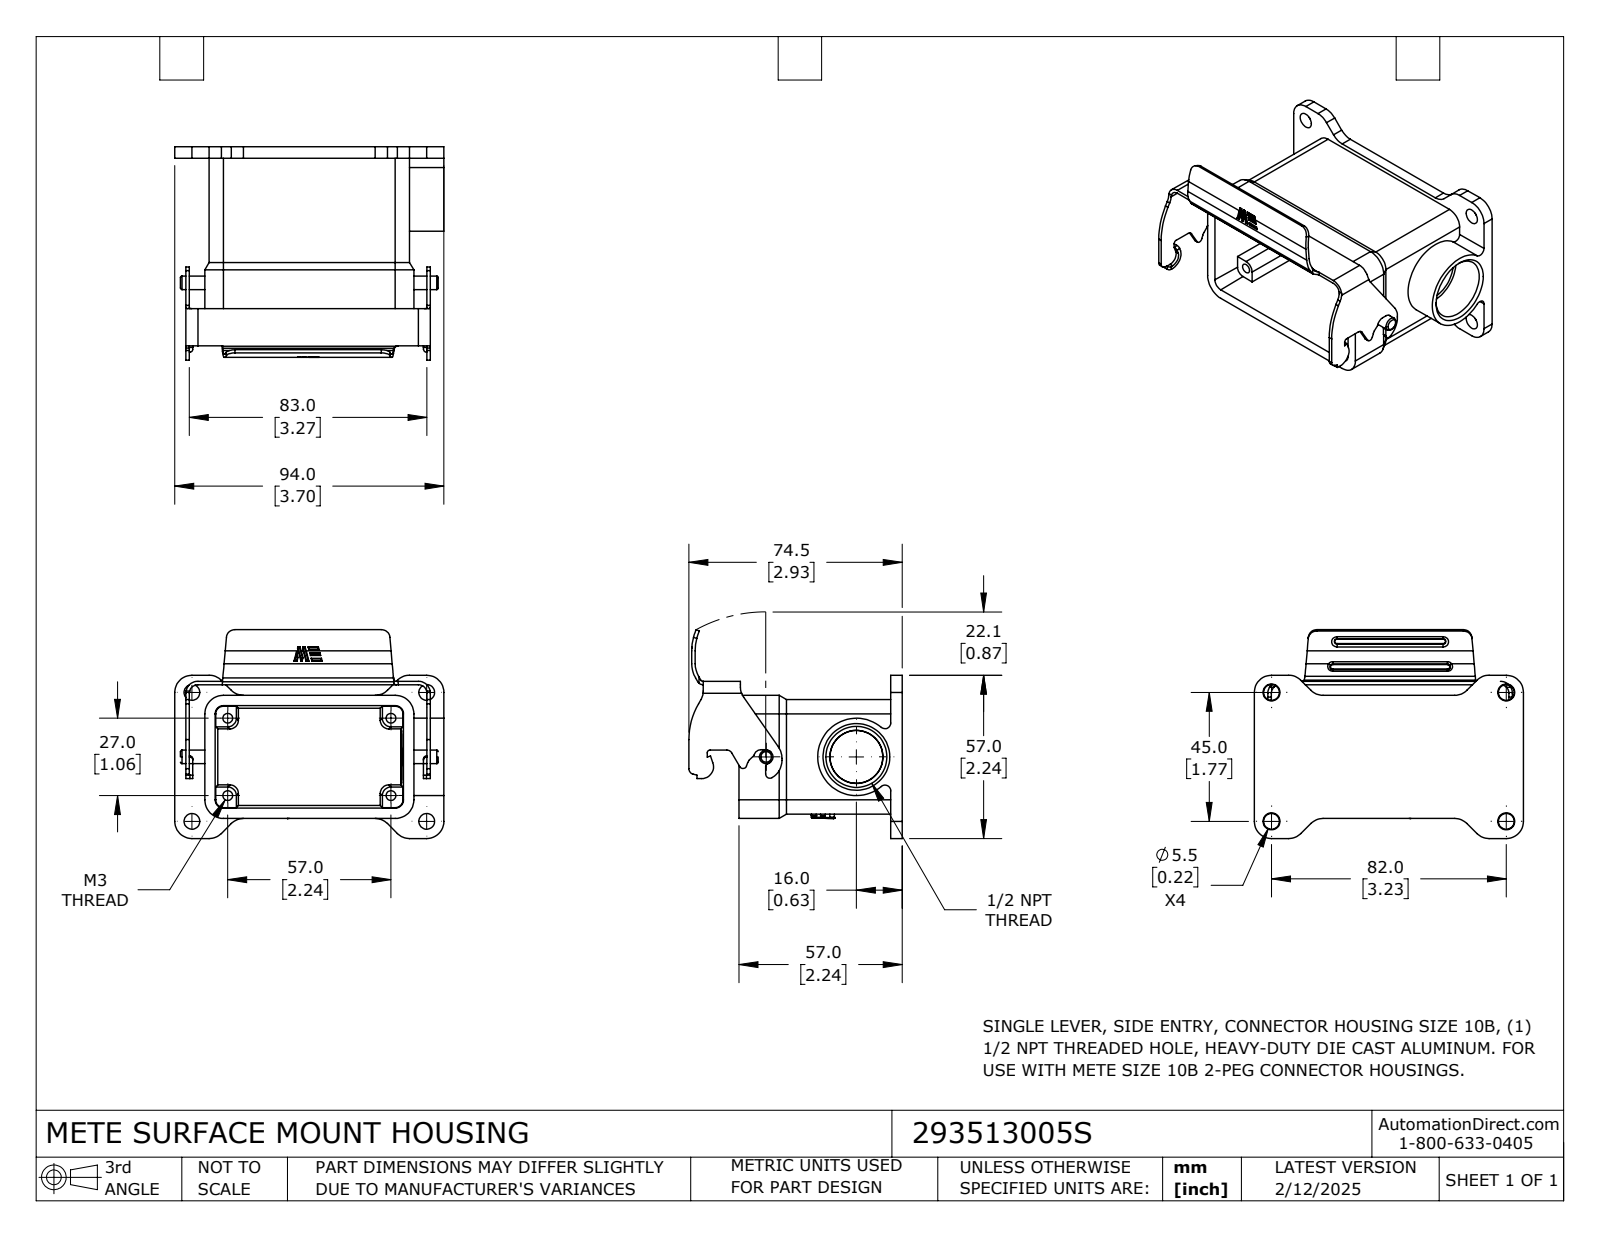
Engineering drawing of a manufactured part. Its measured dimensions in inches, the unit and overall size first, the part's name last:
Units: inches
Overall size (bounding box): 3.701 × 2.933 × 2.87
Round holes (diameter × count): ⌀0.134 ×4, ⌀0.839 ×1
Round bosses / shafts (diameter × count): ⌀0.185 ×1
Partial cylindrical surfaces — rounded edges, fillets, slot ends (radius × count): R0.008 ×46, R0.236 ×14, R0.039 ×10, R0.118 ×9, R0.079 ×5, R0.197 ×4, R0.256 ×4, R0.031 ×3
Main face-to-face distances: 0.157, 0.059, 0.047, 1.575, 1.634, 0.283, 3.315, 1.693, 0.252, 0.205
Hole centre spacings: 1.063, 2.244, 2.483
Volume: 3.937 in³ · Surface area: 64.18 in²
Bodies: 1 solid, 355 faces (149 planar, 164 cylindrical, 42 other)
Part name (STEP PRODUCT): 293513005S
STEP written by: SolidWorks 2024 (CONFIG_CONTROL_DESIGN)
